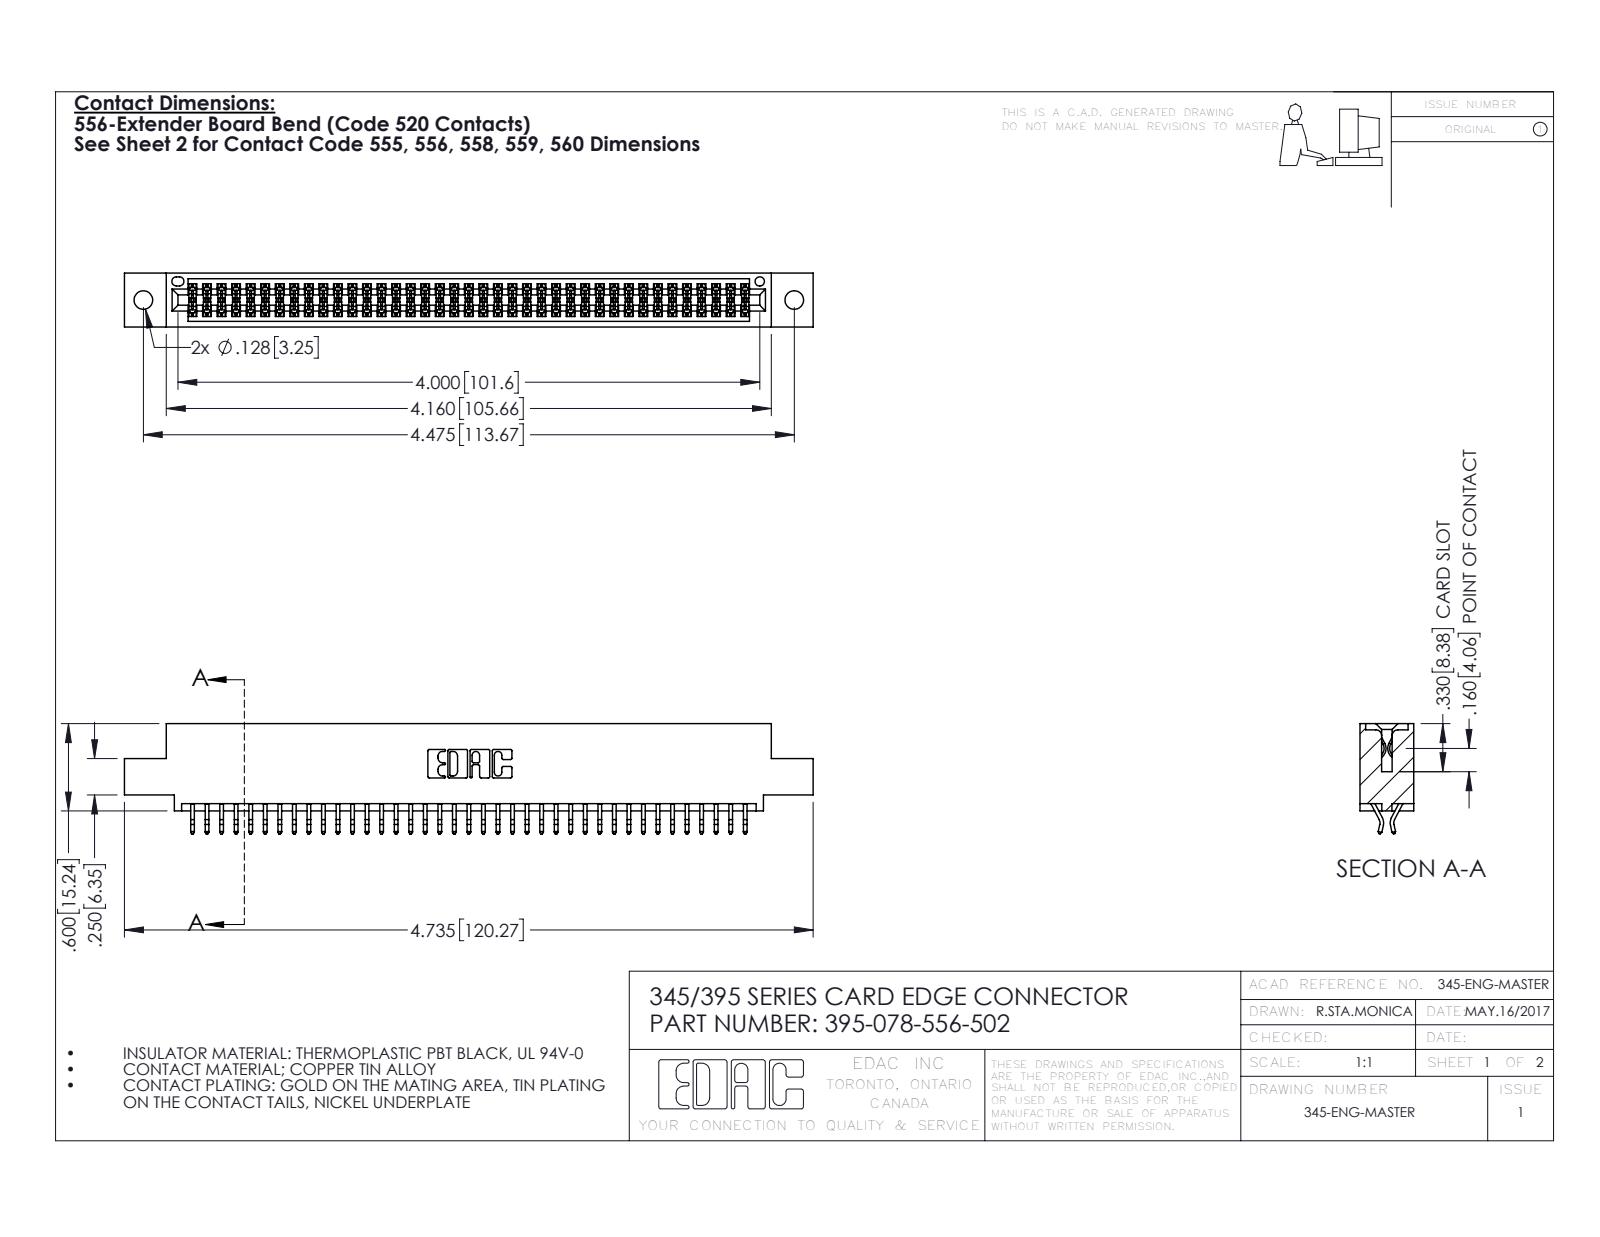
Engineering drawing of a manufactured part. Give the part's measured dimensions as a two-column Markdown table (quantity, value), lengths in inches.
| quantity | value |
| --- | --- |
| part name | 395-078-556-502; 345-292-001_556 Tail; 345 Part_0.110 Offset - 0.128 Dia |
| STEP written by | SolidWorks 2016 (CONFIG_CONTROL_DESIGN) |
| units | inches |
| bodies | 79 solids, 4498 faces (2970 planar, 1528 cylindrical, 0 other) |
| overall size | 4.735 × 0.757 × 0.37 |
| volume | 0.704 in³ |
| surface area | 25.97 in² |
| round holes (diameter × count) | 0.128 × 2, 0.064 × 1 |
| partial cylindrical surfaces (radius × count) | 0.006 × 117, 0.01 × 22, 0.007 × 6, 0.031 × 6, 0.026 × 3, 0.01 × 2, 0.014 × 2, 0.019 × 2 |
| main face-to-face distances | 0.298, 0.072, 0.37, 0.2, 0.025, 0.098, 0.272, 0.225, 0.175, 0.149 |
| hole center spacings | 0.27, 4.239, 4.475 |
